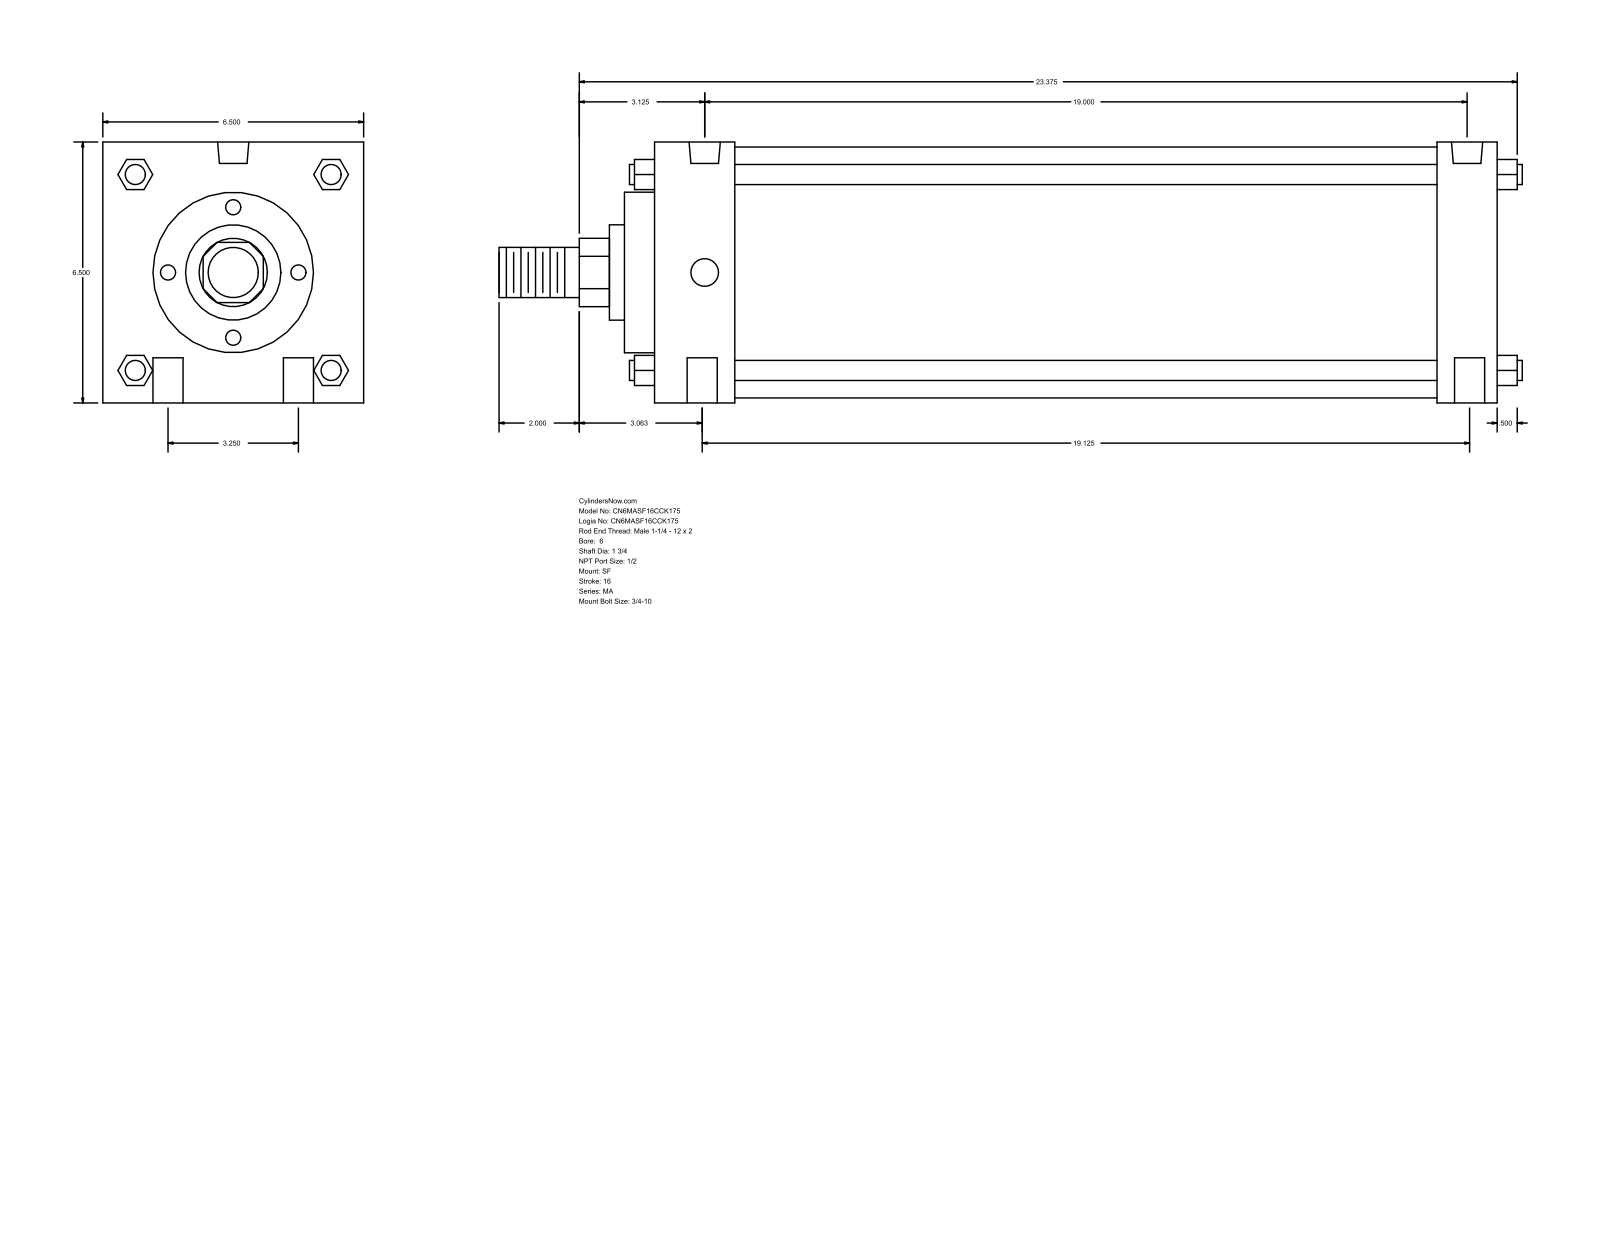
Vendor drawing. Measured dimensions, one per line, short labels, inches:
name: MA_SF__0600_1.75
written by: GSSL Pune (CONFIG_CONTROL_DESIGN)
unit: in
bodies: 0 solids, 126 faces (95 planar, 31 cylindrical, 0 other)
size: 25.5 × 6.5 × 6.5
holes: 4× ⌀0.75, 2× ⌀0.687, 2× ⌀0.778
bosses: 4× ⌀0.5, 1× ⌀6.25, 1× ⌀4, 1× ⌀2.375, 1× ⌀1.75, 1× ⌀1.25
rounds: 1× R0.852
face distances: 6.5, 21, 0.75, 2, 1.5, 19.5, 17.5, 19, 2.75, 20.25
hole spacings: 1.626, 3.25, 19, 19.125, 19.131, 19.132, 19.399
